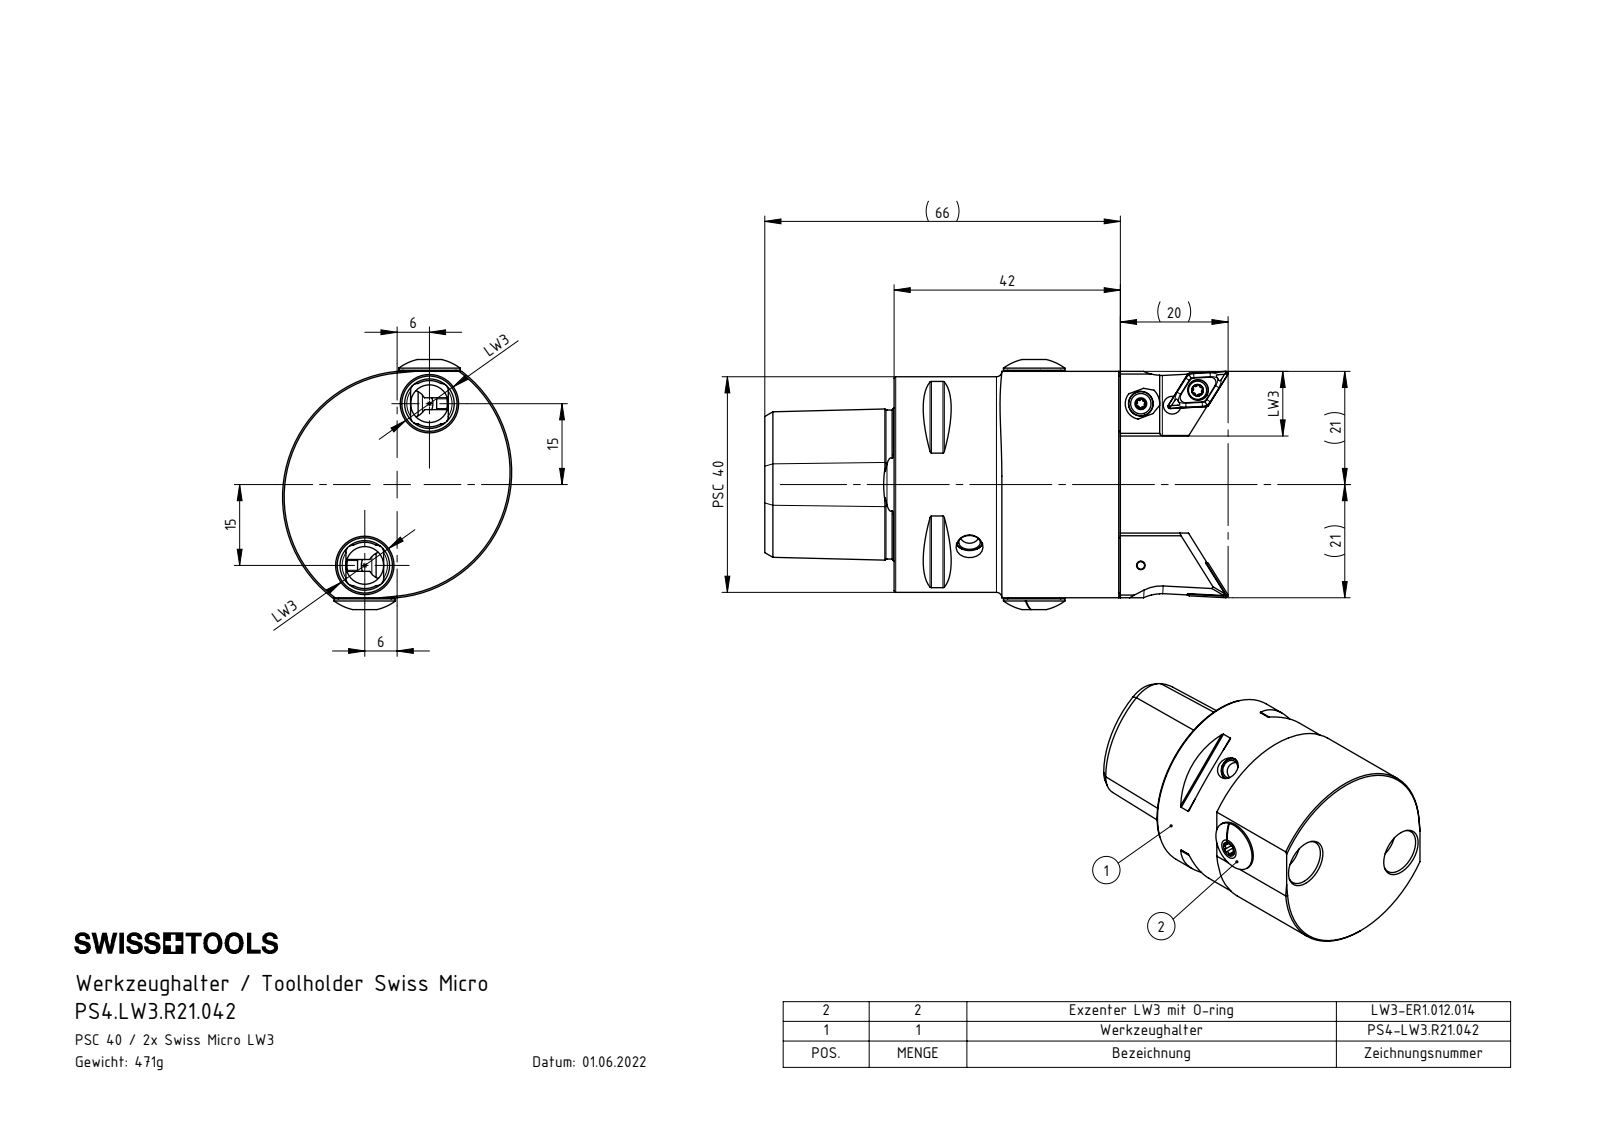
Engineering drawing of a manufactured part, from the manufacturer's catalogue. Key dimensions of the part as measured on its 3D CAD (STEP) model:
Part name (STEP PRODUCT): PS4.LW3.R21.042; PS4-LW3.R21.042_B; LW3-ER1.012.014_E_Standard<Wie bearbeitet>; DIN 3771 - 7x1 (+2 more)
STEP written by: SolidWorks 2022 (AUTOMOTIVE_DESIGN)
Units: millimetres
Bodies: 9 solids, 332 faces (116 planar, 107 cylindrical, 109 other)
Overall size (bounding box): 66 × 46.4 × 42.53
Volume: 59 684 mm³ · Surface area: 16 816 mm²
Round holes (diameter × count): ⌀4.2 ×4, ⌀1 ×2, ⌀2.4 ×2, ⌀5.5 ×2, ⌀7 ×2, ⌀9.21 ×2, ⌀4.6 ×1, ⌀10 ×1, ⌀12.5 ×1, ⌀18 ×1, ⌀20 ×1
Round bosses / shafts (diameter × count): ⌀11.4 ×2, ⌀9.5 ×2, ⌀7.7 ×2, ⌀5 ×2, ⌀40 ×1
Partial cylindrical surfaces — rounded edges, fillets, slot ends (radius × count): R0.34 ×12, R0.59 ×12, R0.3 ×8, R1.3 ×8, R2.5 ×4, R3.6 ×2, R3.7 ×2, R3.75 ×2
Main face-to-face distances: 42, 1.1, 24, 66, 30.4, 11.6, 15.52, 22, 30, 10.2
Hole centre spacings: 16.16, 9.55, 12, 23.5, 32.31
